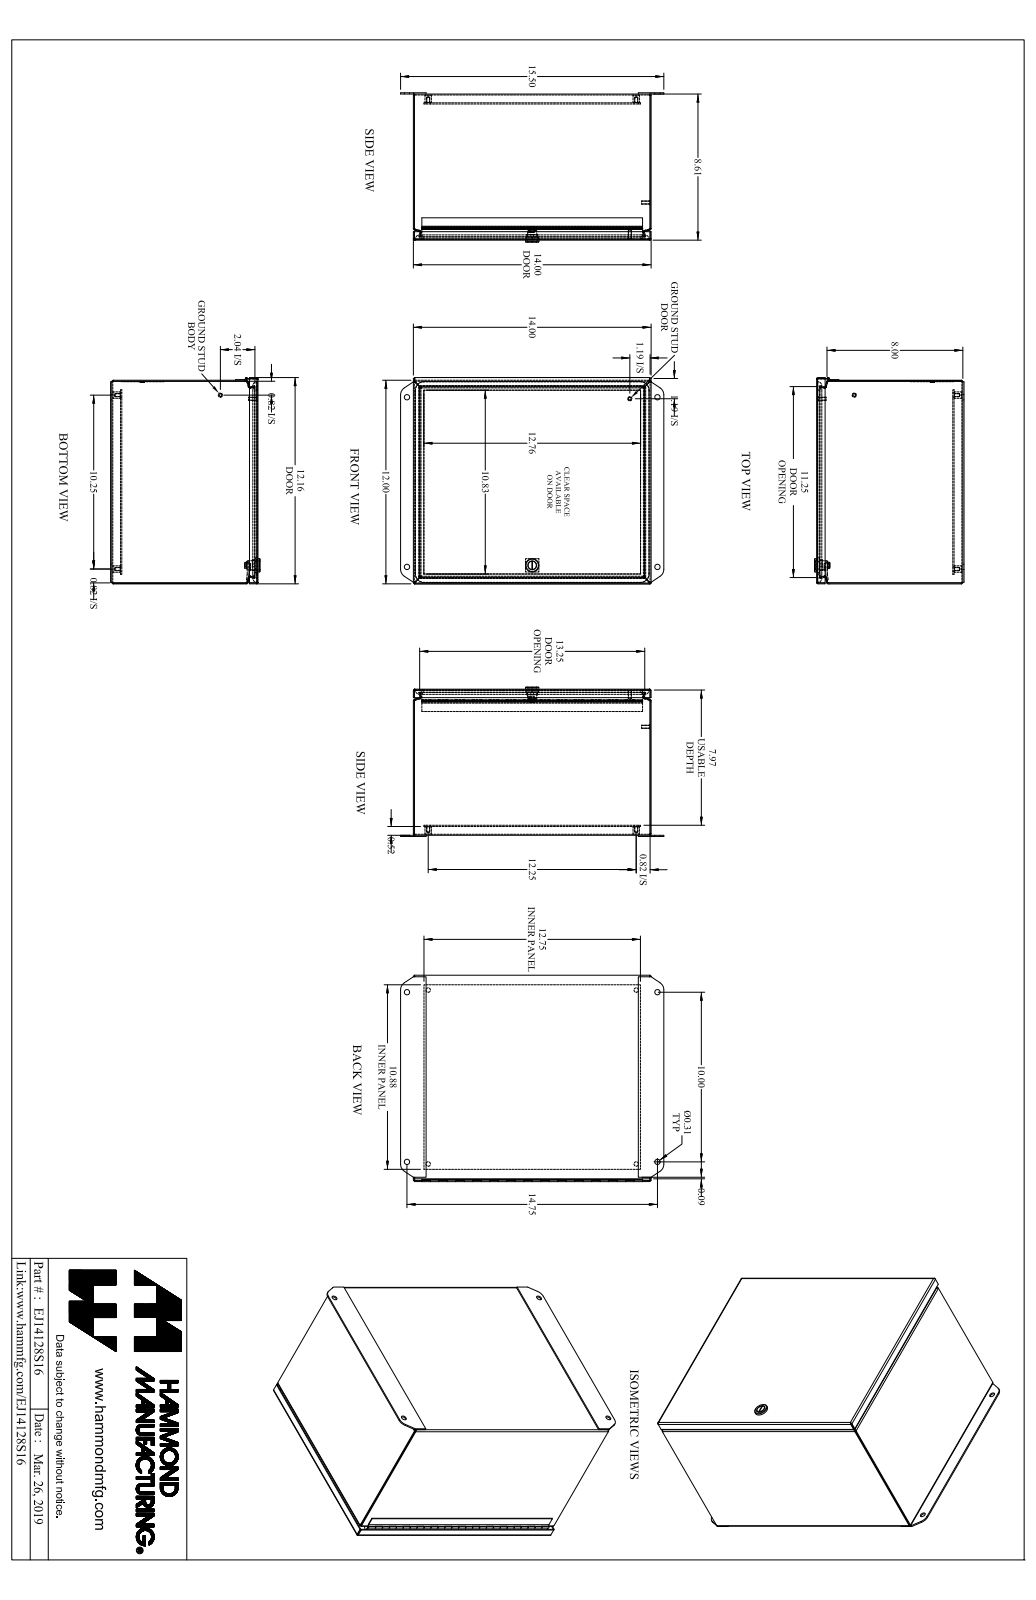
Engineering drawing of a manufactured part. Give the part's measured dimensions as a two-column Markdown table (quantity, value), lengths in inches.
| quantity | value |
| --- | --- |
| part name | EJ14128S16_Default |
| STEP written by | SolidWorks 2019 (CONFIG_CONTROL_DESIGN) |
| units | inches |
| bodies | 16 solids, 660 faces (342 planar, 238 cylindrical, 80 other) |
| overall size | 15.5 × 12.165 × 8.805 |
| volume | 64.08 in³ |
| surface area | 2 129 in² |
| round holes (diameter × count) | 0.156 × 4, 0.265 × 4, 0.313 × 4, 0.05 × 1, 0.516 × 1 |
| round bosses / shafts (diameter × count) | 0.375 × 4, 0.25 × 2, 0.19 × 2, 0.788 × 1, 0.535 × 1, 0.496 × 1, 0.435 × 1, 0.1 × 1 |
| partial cylindrical surfaces (radius × count) | 0.029 × 16, 0.086 × 16, 0.281 × 12, 0.25 × 4, 0.499 × 4, 0.5 × 4, 0.06 × 2, 0.03 × 1 |
| main face-to-face distances | 0.057, 8.554, 11.943, 13.943, 0.072, 0.589, 8.611, 8.497, 8.094, 8.037 |
| hole center spacings | 1.257, 10.202, 13.5, 16.875, 6.129, 7.376, 10, 10.25 |
